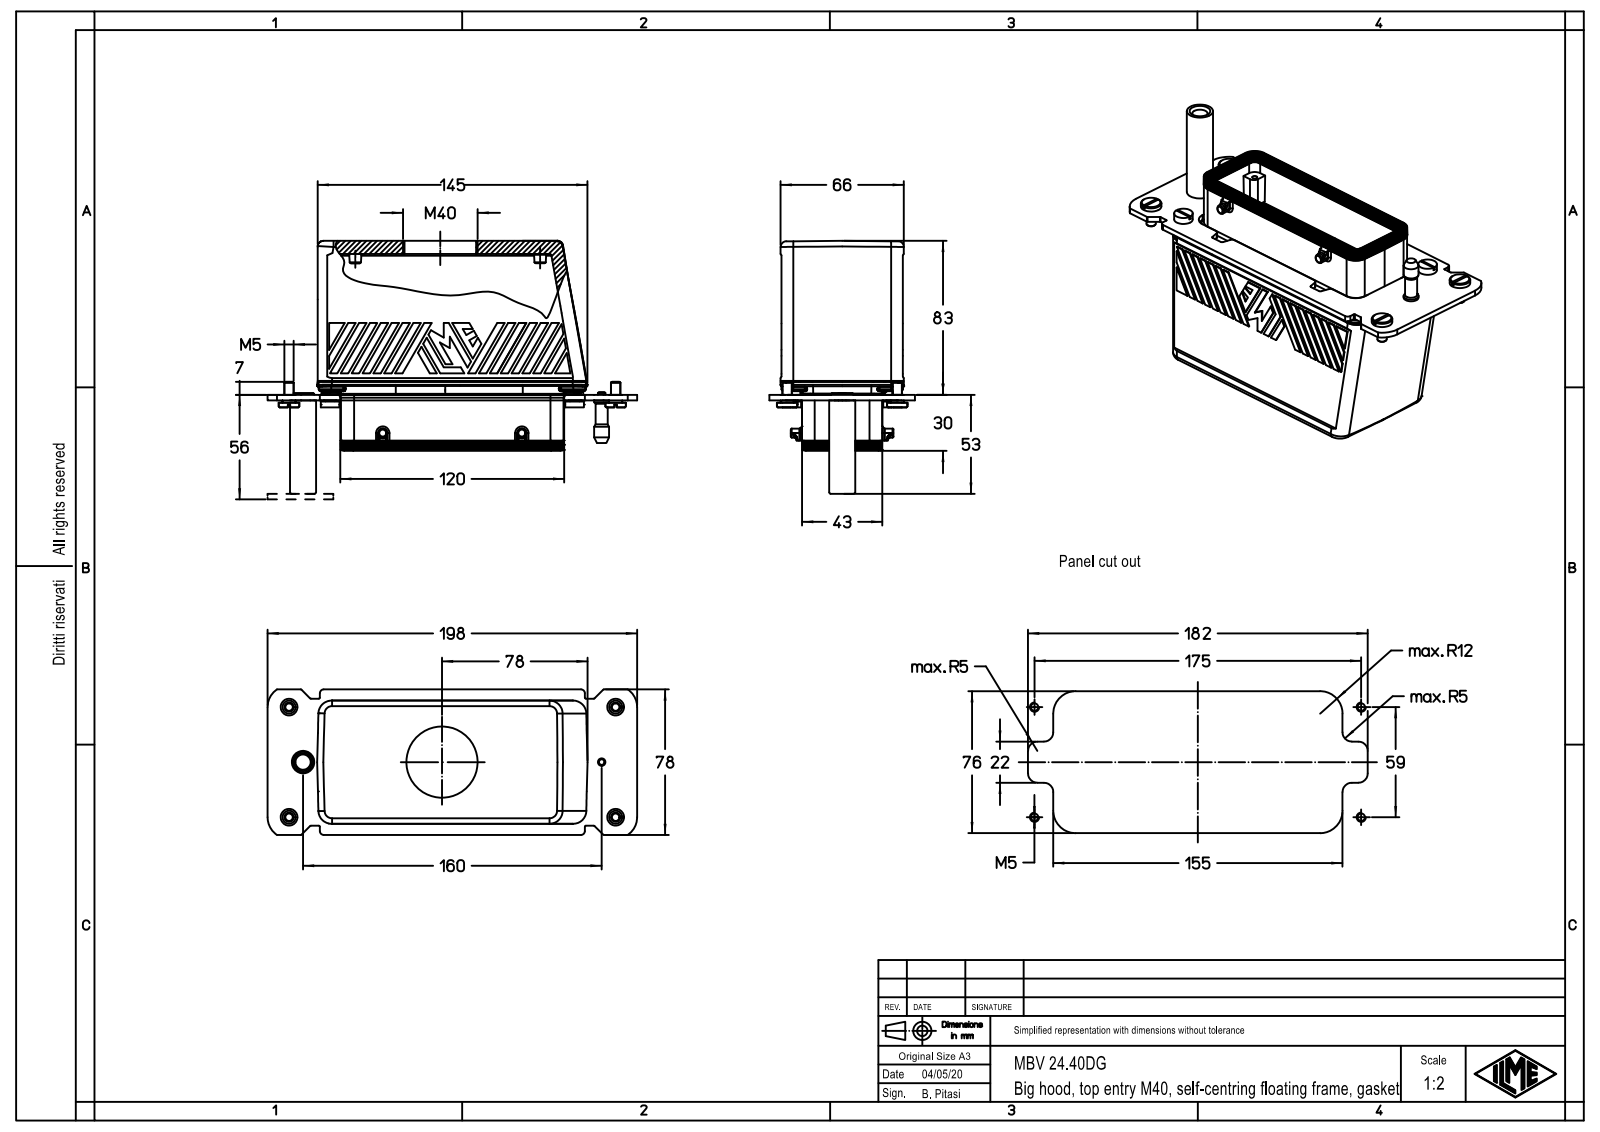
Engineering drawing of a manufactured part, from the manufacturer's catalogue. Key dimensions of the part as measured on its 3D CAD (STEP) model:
Part name (STEP PRODUCT): MBV 24.40DG
STEP written by: Creo Elements/Direct Modeling 20.1B 02-Apr-2019 (C) Parametric Technology GmbH (AUTOMOTIVE_DESIGN)
Units: millimetres
Bodies: 1 solid, 986 faces (508 planar, 250 cylindrical, 228 other)
Overall size (bounding box): 198 × 135.21 × 78
Volume: 759 059 mm³ · Surface area: 102 603 mm²
Round holes (diameter × count): ⌀9 ×4, ⌀5.1 ×2, ⌀7.2 ×2, ⌀4.05 ×1, ⌀8.2 ×1, ⌀9.6 ×1, ⌀12.05 ×1, ⌀40 ×1
Round bosses / shafts (diameter × count): ⌀5 ×6, ⌀11 ×4, ⌀7 ×4, ⌀10 ×2, ⌀9.3 ×2, ⌀4.8 ×2, ⌀14 ×1, ⌀12 ×1
Partial cylindrical surfaces — rounded edges, fillets, slot ends (radius × count): R1 ×52, R0.5 ×20, R7 ×20, R2 ×14, R3 ×10, R4.2 ×8, R0.3 ×6, R1.5 ×6
Main face-to-face distances: 3, 85.21, 82.21, 65.01, 54, 11.01, 0.4, 11.41, 54.4, 65.41
Hole centre spacings: 30.44, 170.08, 22.14, 30.65, 59, 60.63, 147.98, 153.02
